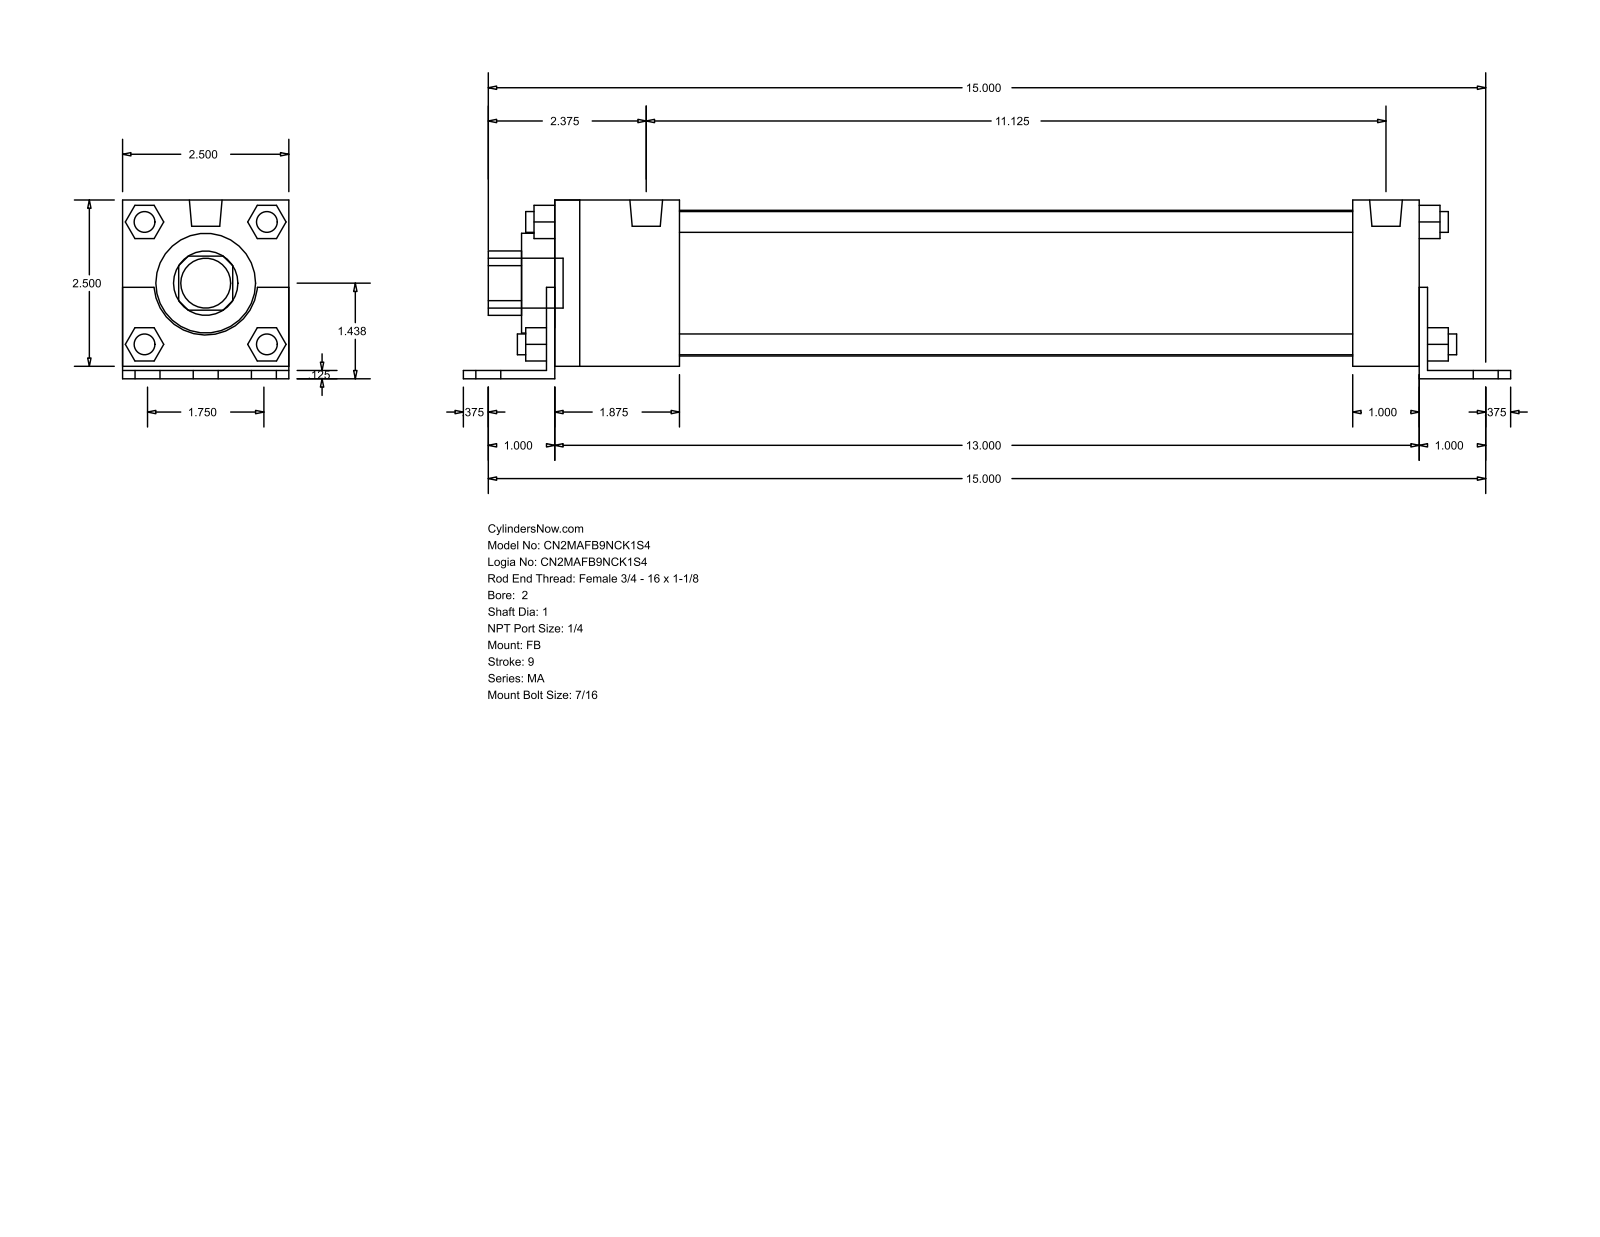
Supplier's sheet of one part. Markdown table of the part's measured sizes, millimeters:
| quantity | value |
| --- | --- |
| part name | MA_FB__0200_1 |
| STEP written by | GSSL Pune (CONFIG_CONTROL_DESIGN) |
| units | millimeters |
| bodies | 0 solids, 140 faces (105 planar, 35 cylindrical, 0 other) |
| overall size | 400.05 × 68.26 × 63.5 |
| round holes (diameter × count) | 25.4 × 1, 38.1 × 1, 55.63 × 1 |
| round bosses / shafts (diameter × count) | 7.94 × 8, 11.11 × 6, 12.49 × 2, 19.05 × 1 |
| partial cylindrical surfaces (radius × count) | 12.29 × 1, 19.81 × 1 |
| main face-to-face distances | 63.5, 3.17, 4.76, 68.26, 1.59, 65.09, 333.37, 12.7, 330.2, 25.4 |
